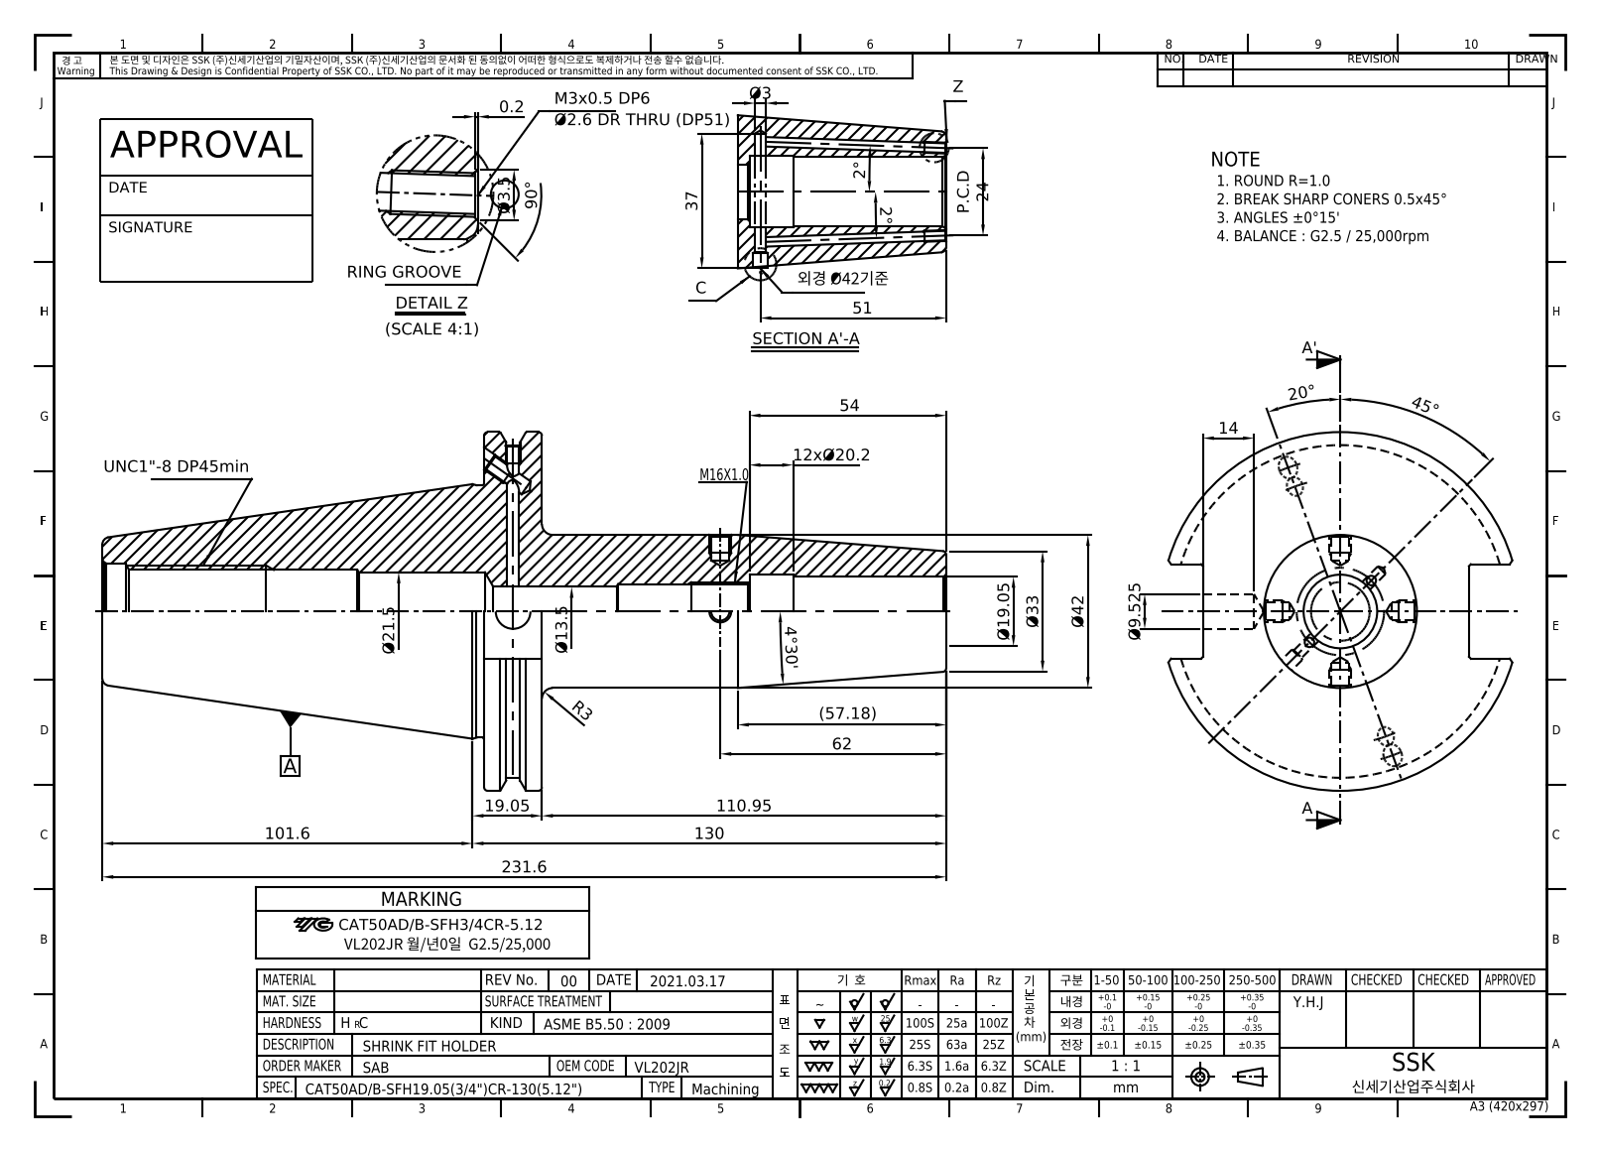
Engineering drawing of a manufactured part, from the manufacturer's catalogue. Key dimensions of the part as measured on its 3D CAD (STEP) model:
Part name (STEP PRODUCT): CAT50ADB-SFH19.05CR-130
STEP written by: Autodesk Inventor 2020 (AUTOMOTIVE_DESIGN)
Units: millimetres
Bodies: 1 solid, 87 faces (37 planar, 28 cylindrical, 22 other)
Overall size (bounding box): 231.6 × 98.42 × 94.69
Volume: 434 885 mm³ · Surface area: 63 722 mm²
Round holes (diameter × count): ⌀3.24 ×2, ⌀4.13 ×2, ⌀4.2 ×2, ⌀5 ×2, ⌀9.53 ×1, ⌀13.5 ×1, ⌀14.92 ×1, ⌀19.05 ×1, ⌀20.2 ×1, ⌀21.5 ×1, ⌀21.97 ×1, ⌀26.2 ×1
Round bosses / shafts (diameter × count): ⌀98.42 ×1, ⌀91.29 ×1, ⌀69.25 ×1, ⌀42 ×1
Main face-to-face distances: 15.88, 104.77, 120.65, 231.6, 126.83, 110.95, 73.03, 25.9, 110.82, 6.05
